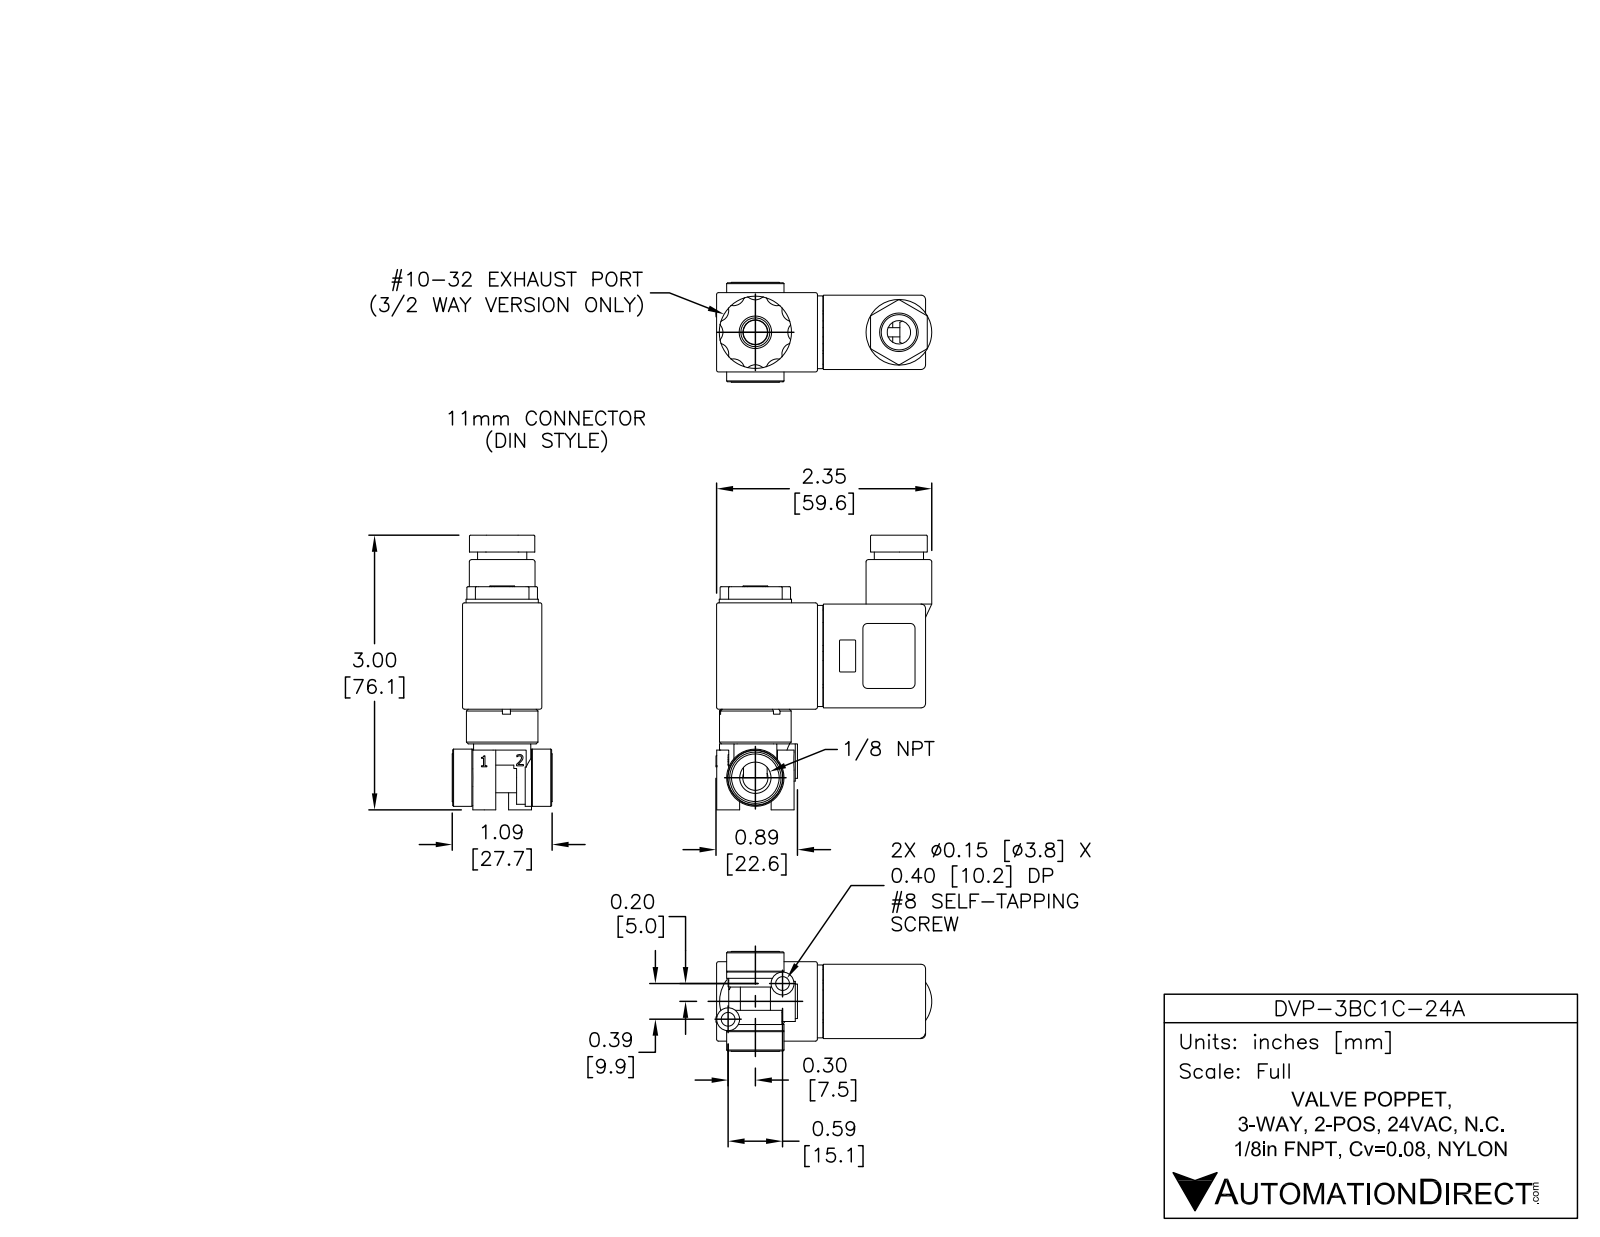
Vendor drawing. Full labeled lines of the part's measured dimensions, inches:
Part name (STEP PRODUCT): DVP-3BC1C-24A
STEP written by: SolidWorks 2015 (AUTOMOTIVE_DESIGN)
Units: inches
Bodies: 9 solids, 1371 faces (689 planar, 261 cylindrical, 421 other)
Overall size (bounding box): 2.988 × 2.354 × 1.09
Volume: 2.034 in³ · Surface area: 34.24 in²
Round holes (diameter × count): ⌀0.1 ×2, ⌀0.125 ×2, ⌀0.15 ×2, ⌀0.057 ×1, ⌀0.062 ×1, ⌀0.09 ×1, ⌀0.102 ×1, ⌀0.165 ×1, ⌀0.196 ×1, ⌀0.204 ×1, ⌀0.255 ×1, ⌀0.268 ×1
Round bosses / shafts (diameter × count): ⌀0.25 ×3, ⌀0.625 ×2, ⌀0.788 ×1, ⌀0.781 ×1, ⌀0.717 ×1, ⌀0.63 ×1, ⌀0.592 ×1, ⌀0.59 ×1
Partial cylindrical surfaces — rounded edges, fillets, slot ends (radius × count): R0.01 ×46, R0.05 ×16, R0.02 ×12, R0.121 ×12, R0.044 ×3, R0.024 ×2, R0.025 ×2, R0.027 ×2
Main face-to-face distances: 0.06, 0.087, 0.779, 0.028, 0.839, 0.751, 0.866, 0.037, 0.829, 0.801
Hole centre spacings: 0.355, 0.175, 0.23, 0.51, 0.57, 0.71, 0.726, 0.997
